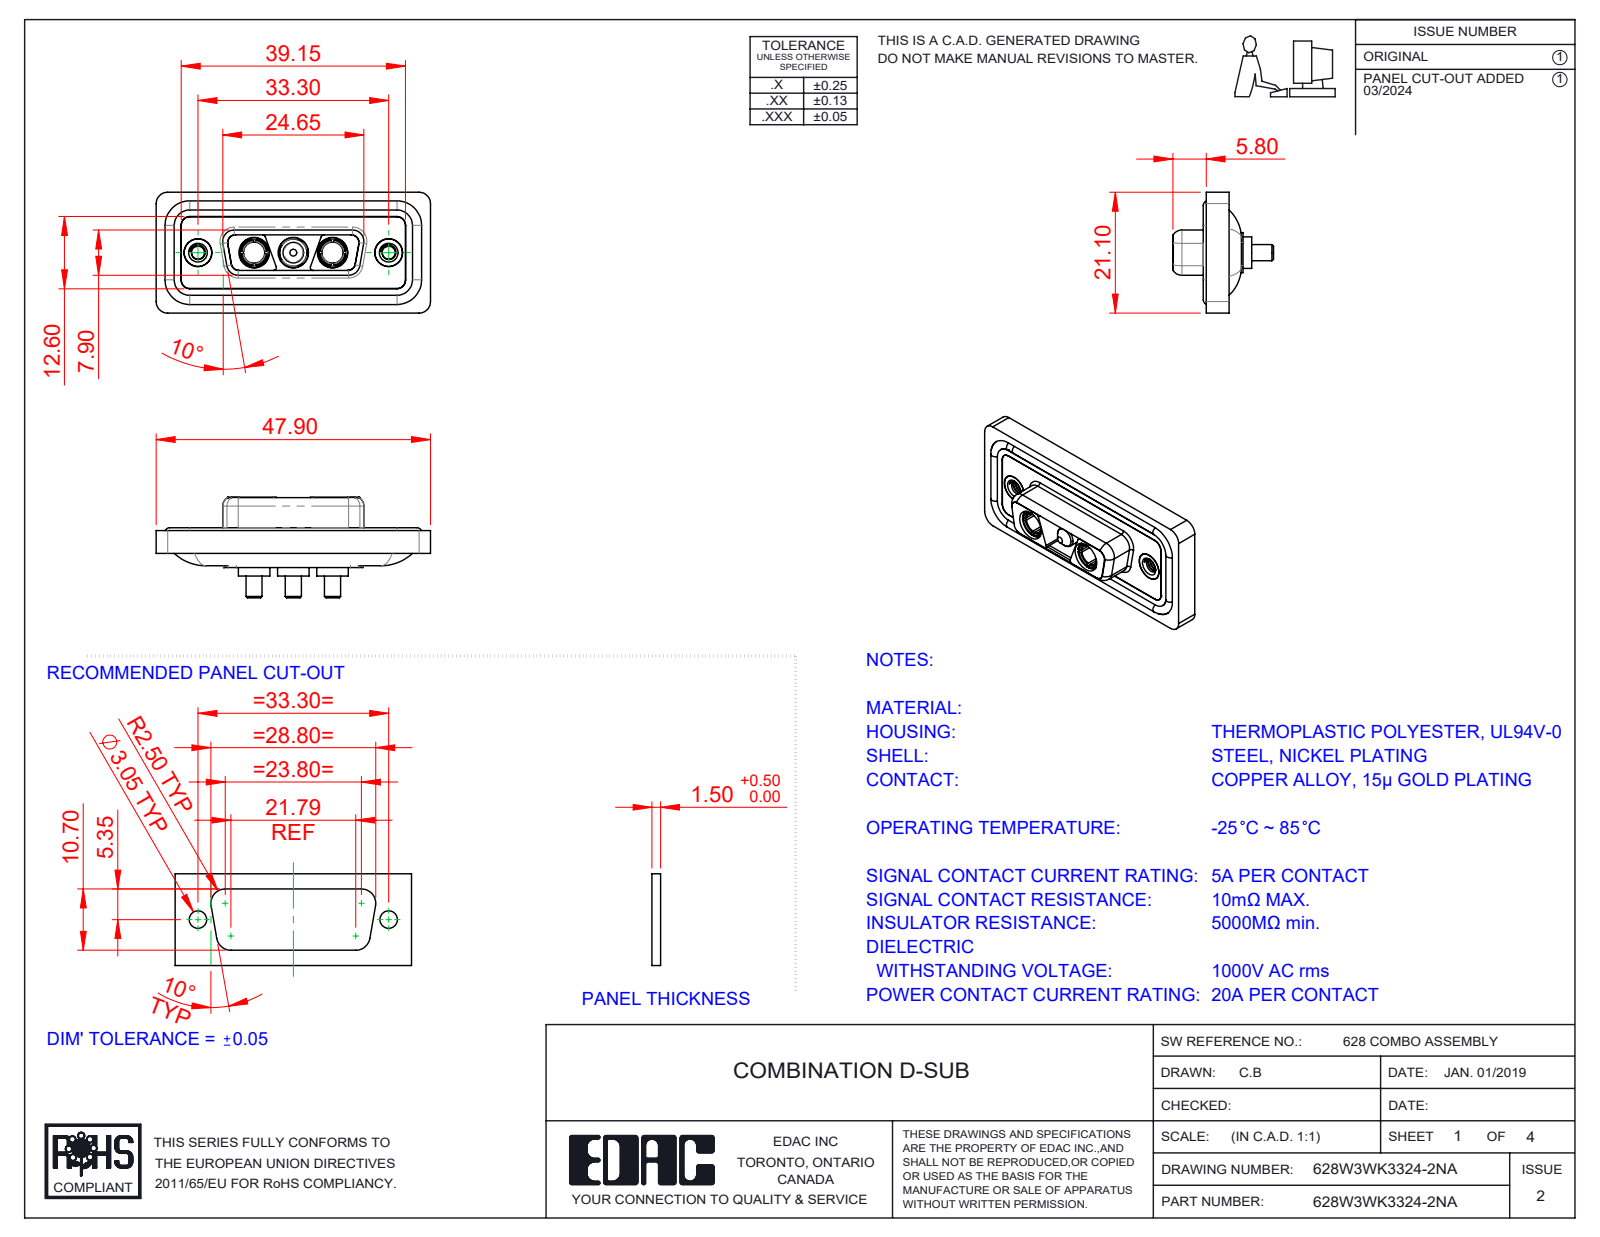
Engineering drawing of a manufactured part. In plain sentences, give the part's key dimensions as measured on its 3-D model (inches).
The part is named "628Combo Waterproof Housing_15 Contacts; 628Combo Housing_3WK3; 628Combo Shell Rear_15 Contacts; Power Pin_20A S (+4 more)". Its 3-D file was written by "SolidWorks 2023 (CONFIG_CONTROL_DESIGN)". It is 13 solids with 581 faces: 178 planar, 260 cylindrical and 143 other. Overall it measures 1.886 by 0.831 by 0.691 inches. Its volume is 0.359 cubic inches and its surface area 14.73 square inches. Round holes: 5 of diameter 0.191, 3 of diameter 0.209, 2 of diameter 0.089, 2 of diameter 0.146, 2 of diameter 0.157, 2 of diameter 0.159, 2 of diameter 0.197. Round bosses or shafts: 4 of diameter 0.063, 3 of diameter 0.217, 3 of diameter 0.205, 3 of diameter 0.187, 3 of diameter 0.148, 3 of diameter 0.11, 2 of diameter 0.195, 2 of diameter 0.195. Partial cylindrical surfaces (rounded edges, fillets, slot ends): 22 of radius 0.059, 20 of radius 0.079, 12 of radius 0.053, 8 of radius 0.02, 8 of radius 0.063, 4 of radius 0.01, 4 of radius 0.024, 4 of radius 0.026. The main face-to-face distances are 0.016, 0.063, 0.071, 0.02, 0.043, 0.114, 0.222, 0.278, 0.059, 0.211. The hole center spacings are 0.27, 0.386, 0.656, 0.925, 0.539, 1.311.
